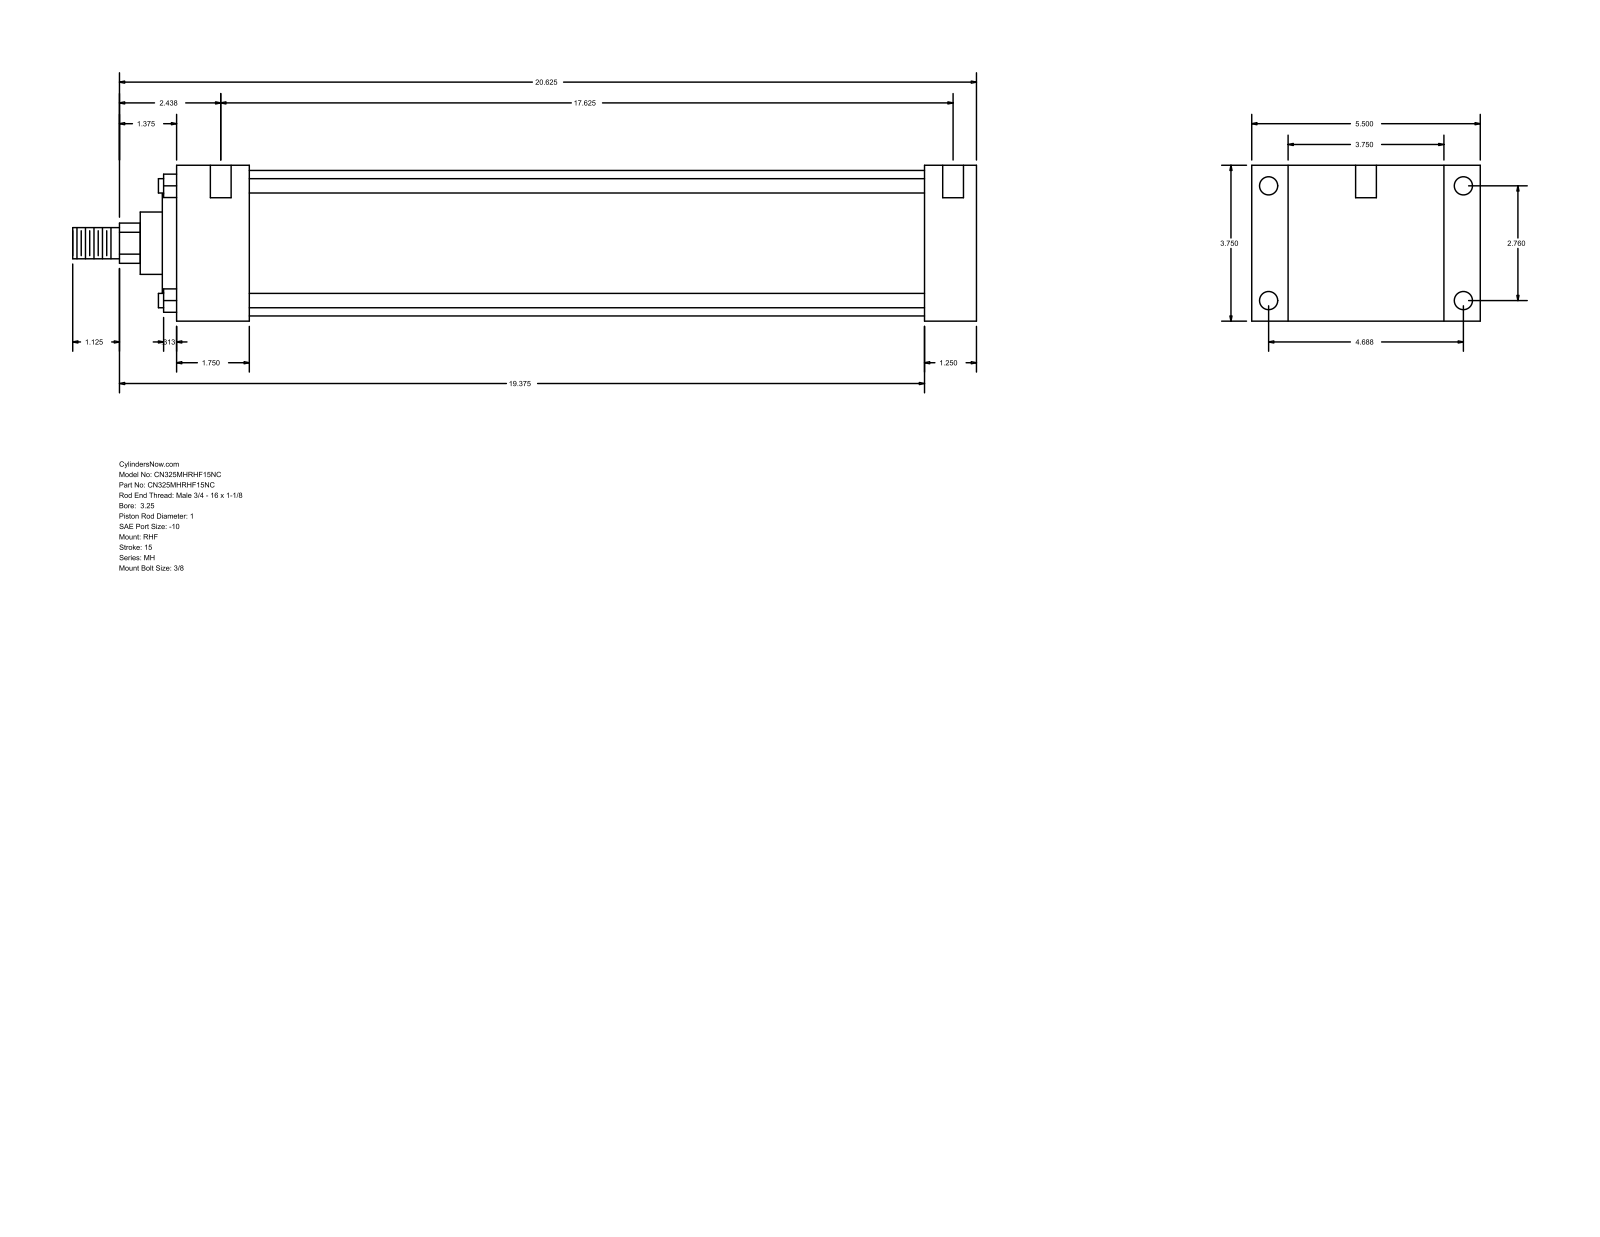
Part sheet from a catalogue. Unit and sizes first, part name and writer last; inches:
Units: inches
Overall size (bounding box): 21.75 × 5.5 × 3.75
Round holes (diameter × count): ⌀0.219 ×4, ⌀0.438 ×4, ⌀0.5 ×2
Round bosses / shafts (diameter × count): ⌀0.345 ×4, ⌀3.5 ×1, ⌀2.375 ×1, ⌀1.5 ×1, ⌀1 ×1, ⌀0.75 ×1
Partial cylindrical surfaces — rounded edges, fillets, slot ends (radius × count): R0.484 ×1
Main face-to-face distances: 3.75, 1.25, 0.875, 4.625, 18, 19.25, 5.5, 1.75, 16.25, 17.5
Hole centre spacings: 2.76, 4.687, 5.439, 17.875, 0.062, 0.187, 17.625, 17.687
Bodies: 0 solids, 90 faces (61 planar, 29 cylindrical, 0 other)
Part name (STEP PRODUCT): MH_RHF__0325_1
STEP written by: GSSL Pune (CONFIG_CONTROL_DESIGN)
